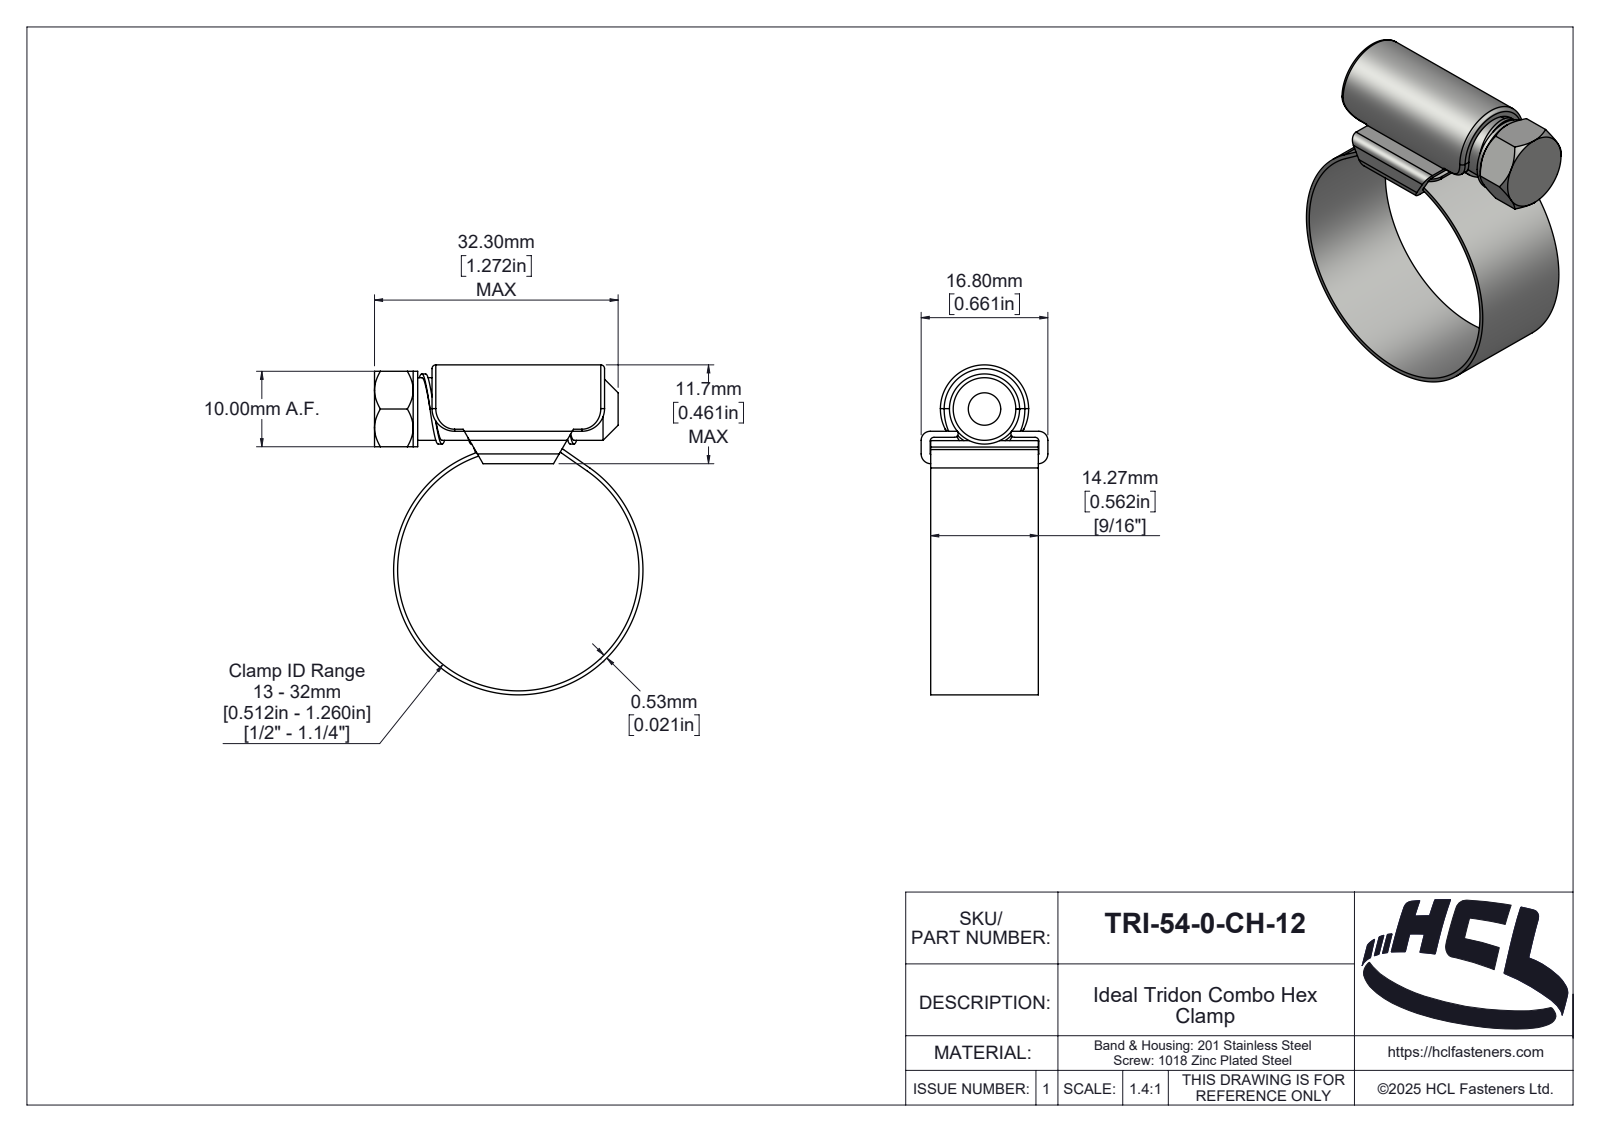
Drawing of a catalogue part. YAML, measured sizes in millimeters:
part_name: "TRI-54-0-CH-12"
step_written_by: "SolidWorks 2025 (AUTOMOTIVE_DESIGN)"
units: millimeters
bodies: {solids: 3, faces: 212, planar: 35, cylindrical: 101, other: 76}
overall_size: [43.73, 35.59, 16.8]
volume: 3705
surface_area: 6192
round_holes:
  - {diameter: 32, count: 1}
round_bosses_or_shafts:
  - {diameter: 33.06, count: 1}
  - {diameter: 10, count: 1}
  - {diameter: 8.3, count: 1}
partial_cylinders:
  - {radius: 0.5, count: 6}
  - {radius: 3, count: 4}
  - {radius: 0.1, count: 2}
  - {radius: 1.2, count: 2}
  - {radius: 1.3, count: 2}
  - {radius: 0.46, count: 1}
  - {radius: 1.89, count: 1}
  - {radius: 2, count: 1}
face_to_face_distances: [1.2, 3.5, 2.3, 4.3, 3.1, 0.8, 0.53, 14.26, 9.99, 1.27]
